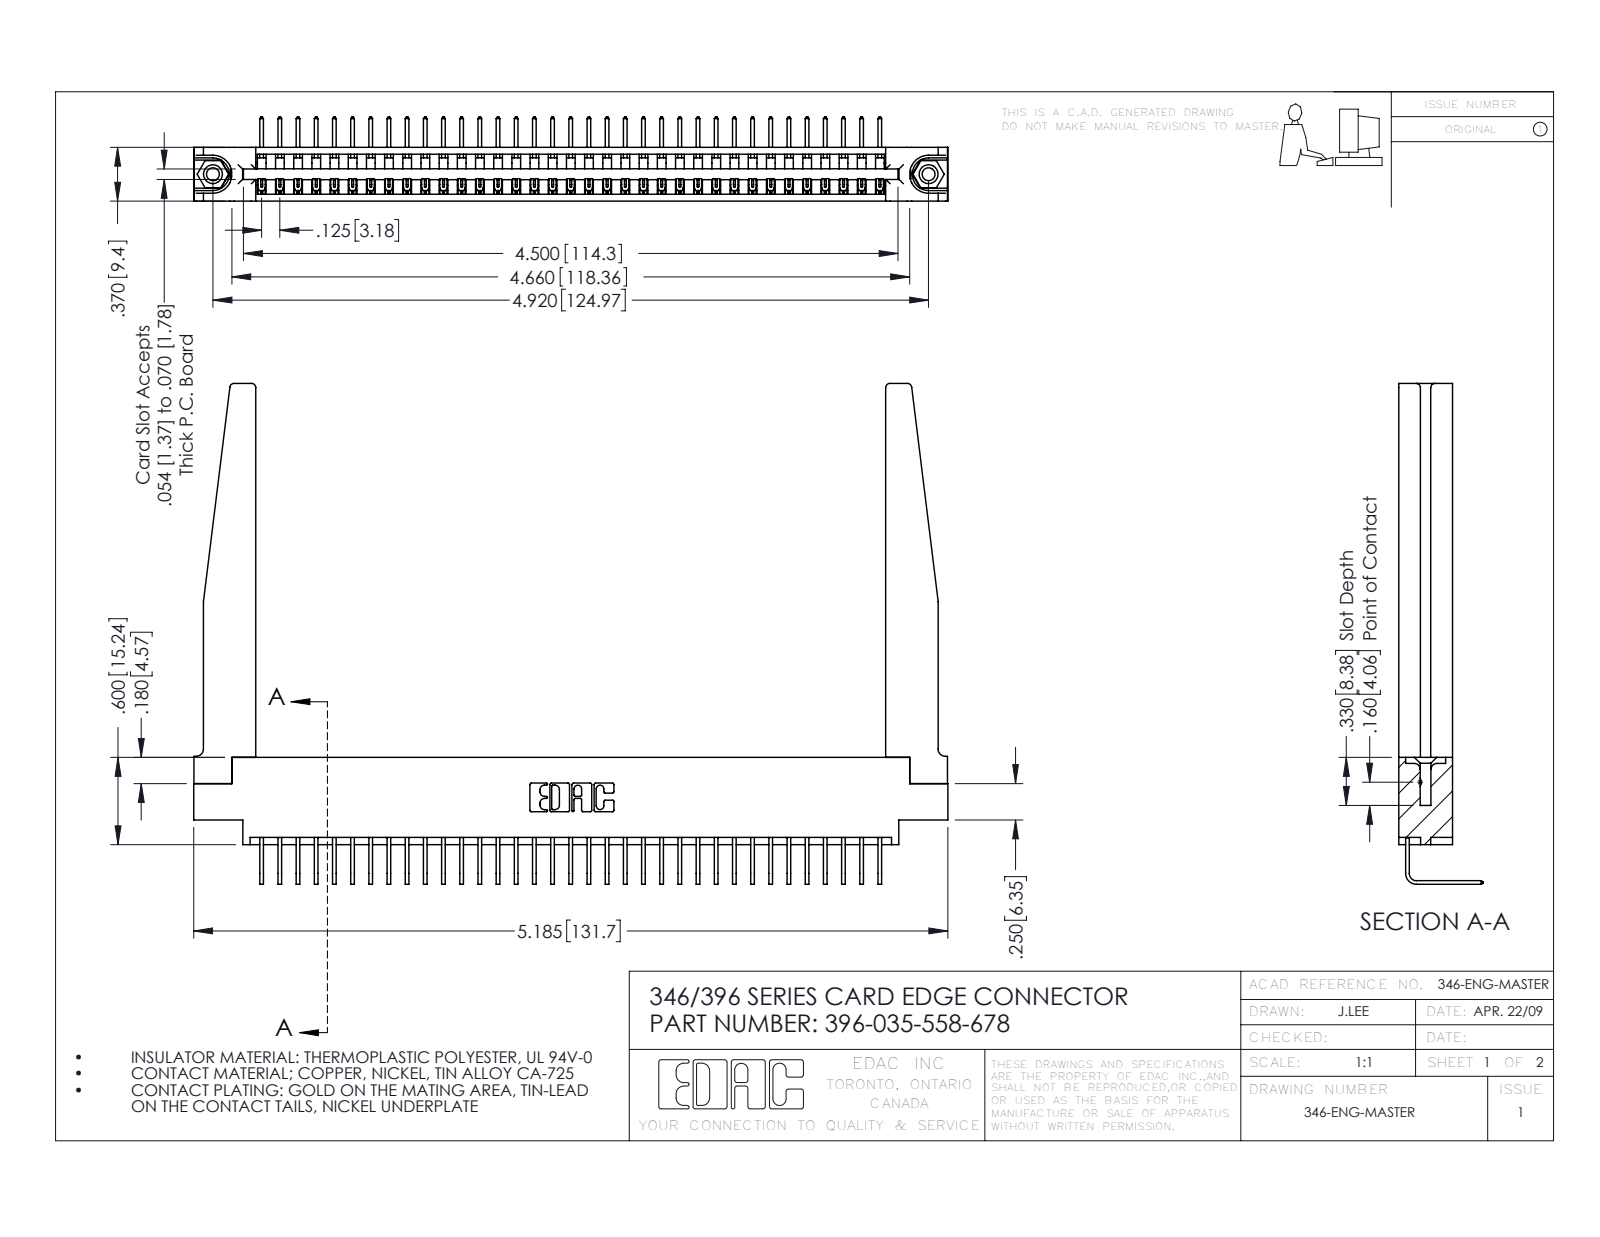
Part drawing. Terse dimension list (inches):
name: 345-292-001_558 Tail - 2; 346 Part_0.170 Offset - 0.156 Dia-TH; 396-035-558-678; 346-220-078_345-220-078 (+1 more)
written by: SolidWorks 2016 (CONFIG_CONTROL_DESIGN)
unit: in
bodies: 40 solids, 2460 faces (1692 planar, 716 cylindrical, 52 other)
size: 5.185 × 3.443 × 0.58
volume: 1.186 in³; area: 35.6 in²
holes: 2× ⌀0.089, 2× ⌀0.125, 2× ⌀0.156, 1× ⌀0.064
bosses: 2× ⌀0.155
rounds: 70× R0.006, 22× R0.01, 8× R0.03, 6× R0.007, 6× R0.031, 3× R0.026, 3× R0.05, 2× R0.031
face distances: 0.37, 0.322, 0.048, 0.072, 0.148, 0.15, 0.298, 0.025, 0.25, 0.222
hole spacings: 0.246, 4.711, 4.92
